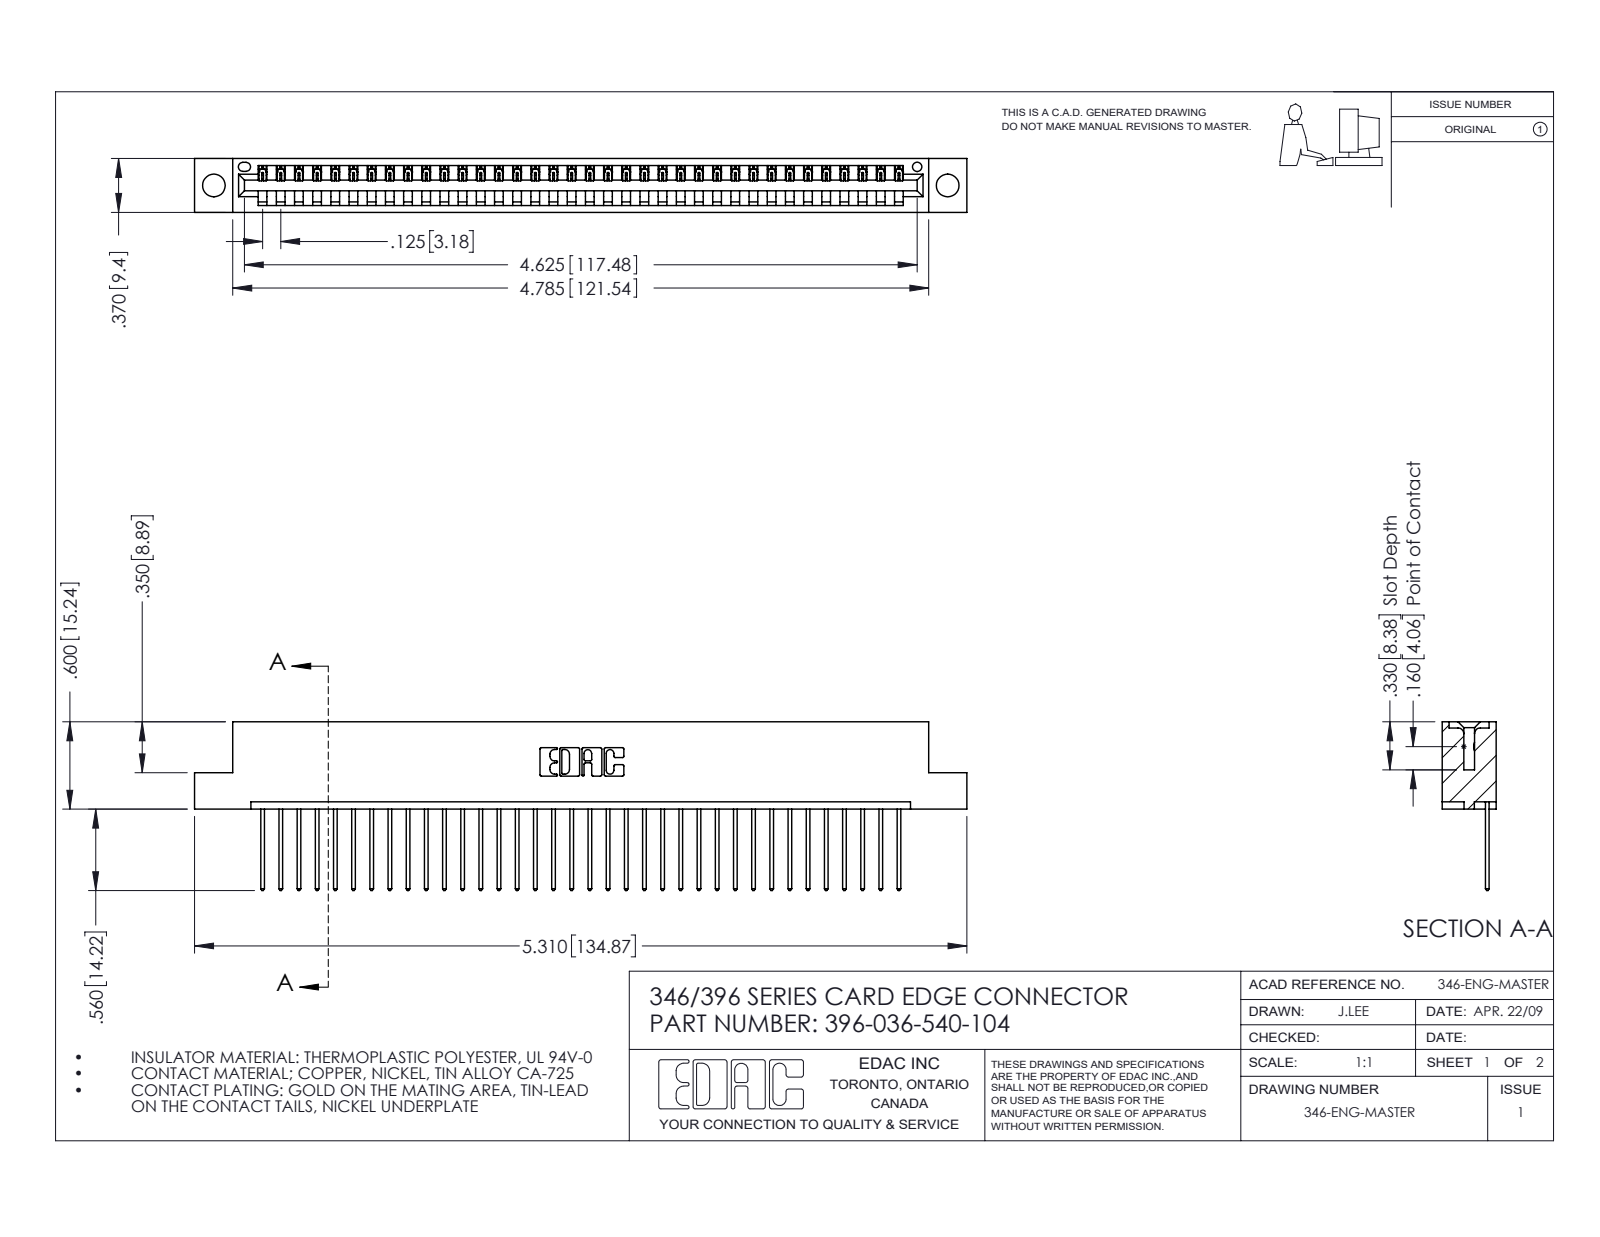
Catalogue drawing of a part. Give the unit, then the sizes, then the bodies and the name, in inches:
Units: inches
Overall size (bounding box): 5.31 × 1.16 × 0.37
Round holes (diameter × count): ⌀0.156 ×2, ⌀0.064 ×1
Partial cylindrical surfaces — rounded edges, fillets, slot ends (radius × count): R0.006 ×72, R0.01 ×72, R0.01 ×22, R0.007 ×6, R0.031 ×6, R0.026 ×3, R0.031 ×2, R0.04 ×2
Main face-to-face distances: 0.048, 0.322, 0.37, 0.25, 0.072, 0.298, 0.025, 0.148, 0.222, 0.1
Hole centre spacings: 0.246, 4.836, 5.045
Volume: 0.783 in³ · Surface area: 25 in²
Bodies: 37 solids, 2210 faces (1516 planar, 694 cylindrical, 0 other)
Part name (STEP PRODUCT): 346 Part_Flush Mounting Lugs - 0.156 Dia-TH; 345-292-001_345-293-140; 396-036-540-104
STEP written by: SolidWorks 2016 (CONFIG_CONTROL_DESIGN)
